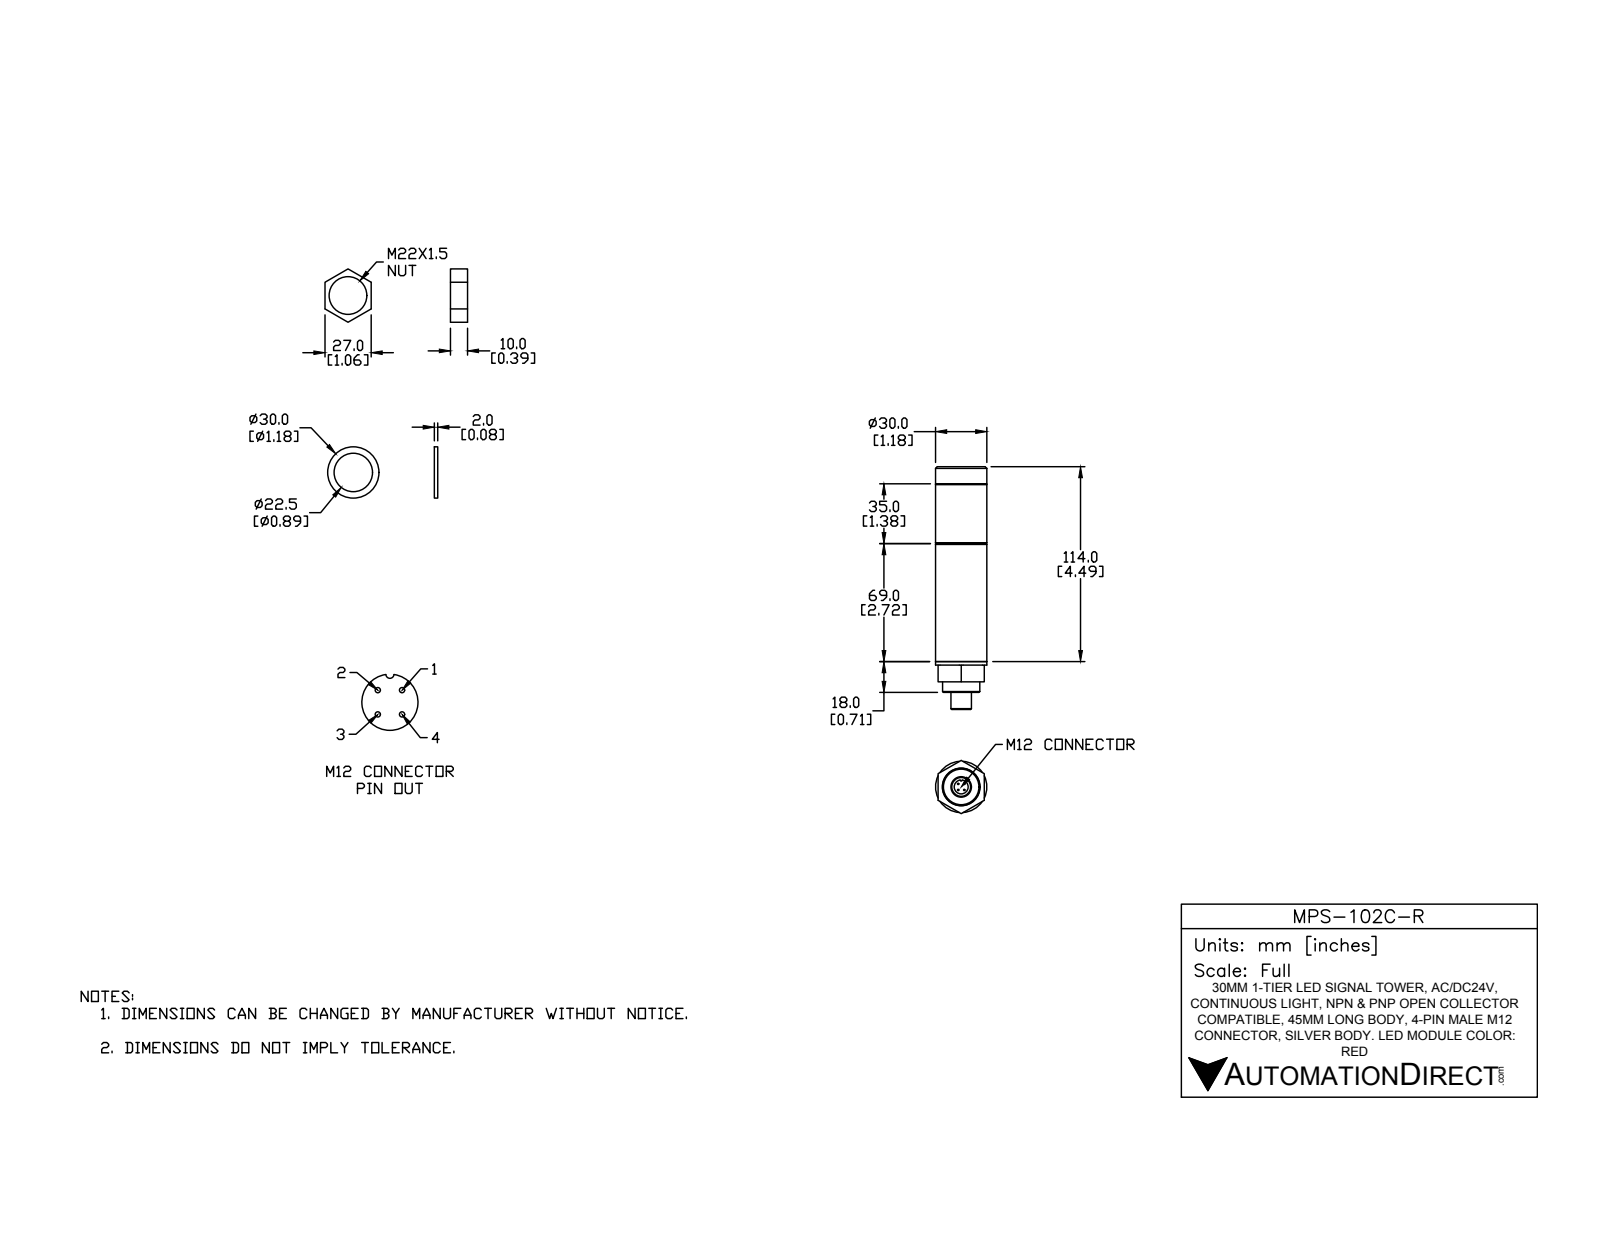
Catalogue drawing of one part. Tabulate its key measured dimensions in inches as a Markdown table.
| quantity | value |
| --- | --- |
| part name | MPS-102C-R |
| STEP written by | SolidWorks 2016 (AUTOMOTIVE_DESIGN) |
| units | inches |
| bodies | 10 solids, 98 faces (41 planar, 35 cylindrical, 22 other) |
| overall size | 5.591 × 1.228 × 1.181 |
| volume | 4.866 in³ |
| surface area | 35.39 in² |
| round holes (diameter × count) | 0.126 × 1, 0.303 × 1, 0.323 × 1, 0.815 × 1, 0.866 × 1 |
| round bosses / shafts (diameter × count) | 0.03 × 4, 1.181 × 1, 0.858 × 1, 0.472 × 1, 0.197 × 1 |
| partial cylindrical surfaces (radius × count) | 0.024 × 1 |
| main face-to-face distances | 1.378, 2.717, 4.094, 2.795, 0.394, 0.079, 4.173, 4.488, 4.567, 1.772 |
